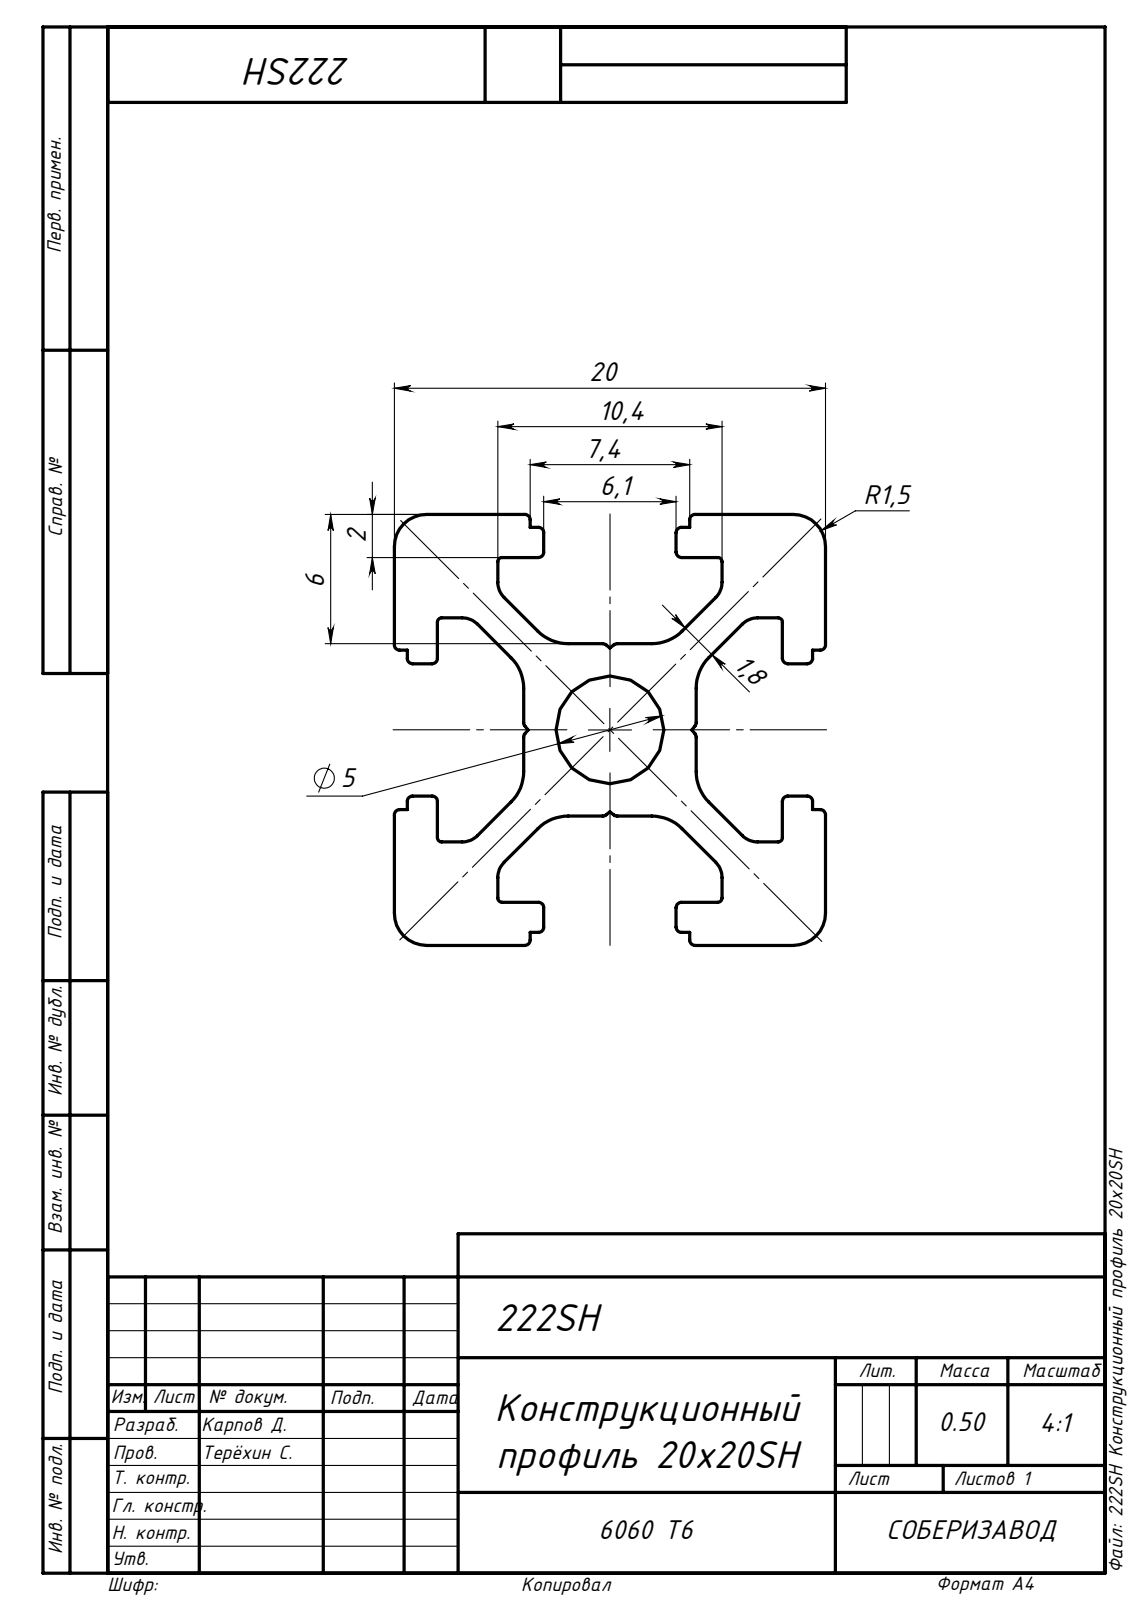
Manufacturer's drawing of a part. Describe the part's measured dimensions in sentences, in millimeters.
Its 3-D file was written by "SolidWorks 2018 (AUTOMOTIVE_DESIGN)". It is 1 solid with 136 faces: 74 planar, 62 cylindrical and 0 other. Overall it measures 1000 by 20 by 20 millimeters. Its volume is 184 055 cubic millimeters and its surface area 160 371 square millimeters. Round holes: 1 of diameter 5. Partial cylindrical surfaces (rounded edges, fillets, slot ends): 32 of radius 0.25, 8 of radius 0.2, 8 of radius 1, 8 of radius 2, 4 of radius 1.5. The main face-to-face distances are 20, 18, 2, 6, 14, 4, 12, 1.74, 4.8, 15.2.
